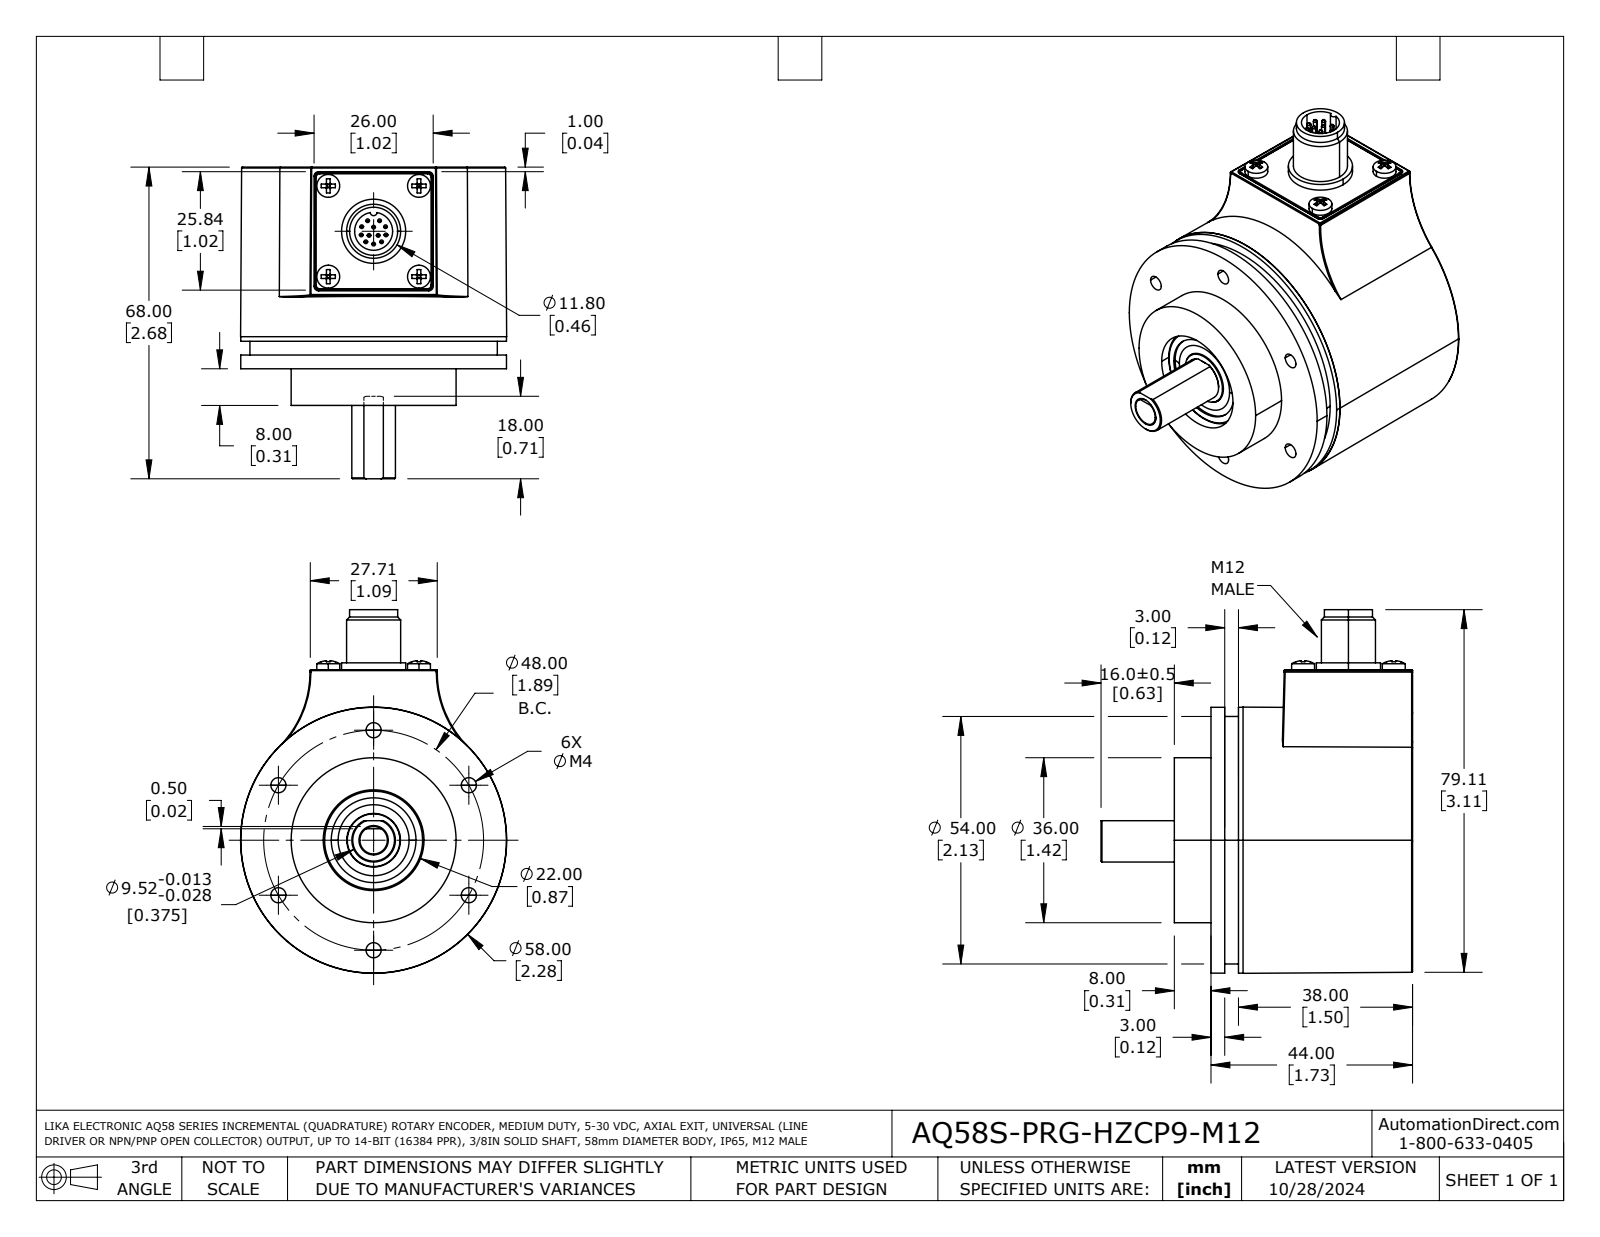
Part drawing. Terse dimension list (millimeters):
name: AQ58S-PRG-HZCP9-M12
written by: SolidWorks 2021 (AUTOMOTIVE_DESIGN)
unit: mm
bodies: 17 solids, 1630 faces (987 planar, 299 cylindrical, 344 other)
size: 79.3 × 68 × 58.1
volume: 48 180 mm³; area: 40 320 mm²
holes: 6× ⌀2.5, 6× ⌀3.3, 4× ⌀3.2, 2× ⌀1.6, 2× ⌀8, 1× ⌀4, 1× ⌀6, 1× ⌀8.3, 1× ⌀10, 1× ⌀11.7, 1× ⌀18.5, 1× ⌀20
bosses: 12× ⌀1.3, 12× ⌀0.8, 4× ⌀5, 4× ⌀2.5, 3× ⌀3, 1× ⌀58, 1× ⌀56, 1× ⌀54
rounds: 35× R0.2, 9× R0.2, 6× R0.5, 1× R0.8
face distances: 3, 34, 44, 10, 1, 31.5, 2, 2.5, 41.5, 7
hole spacings: 24, 25, 13.5, 14, 19.8, 20.7, 21, 28
